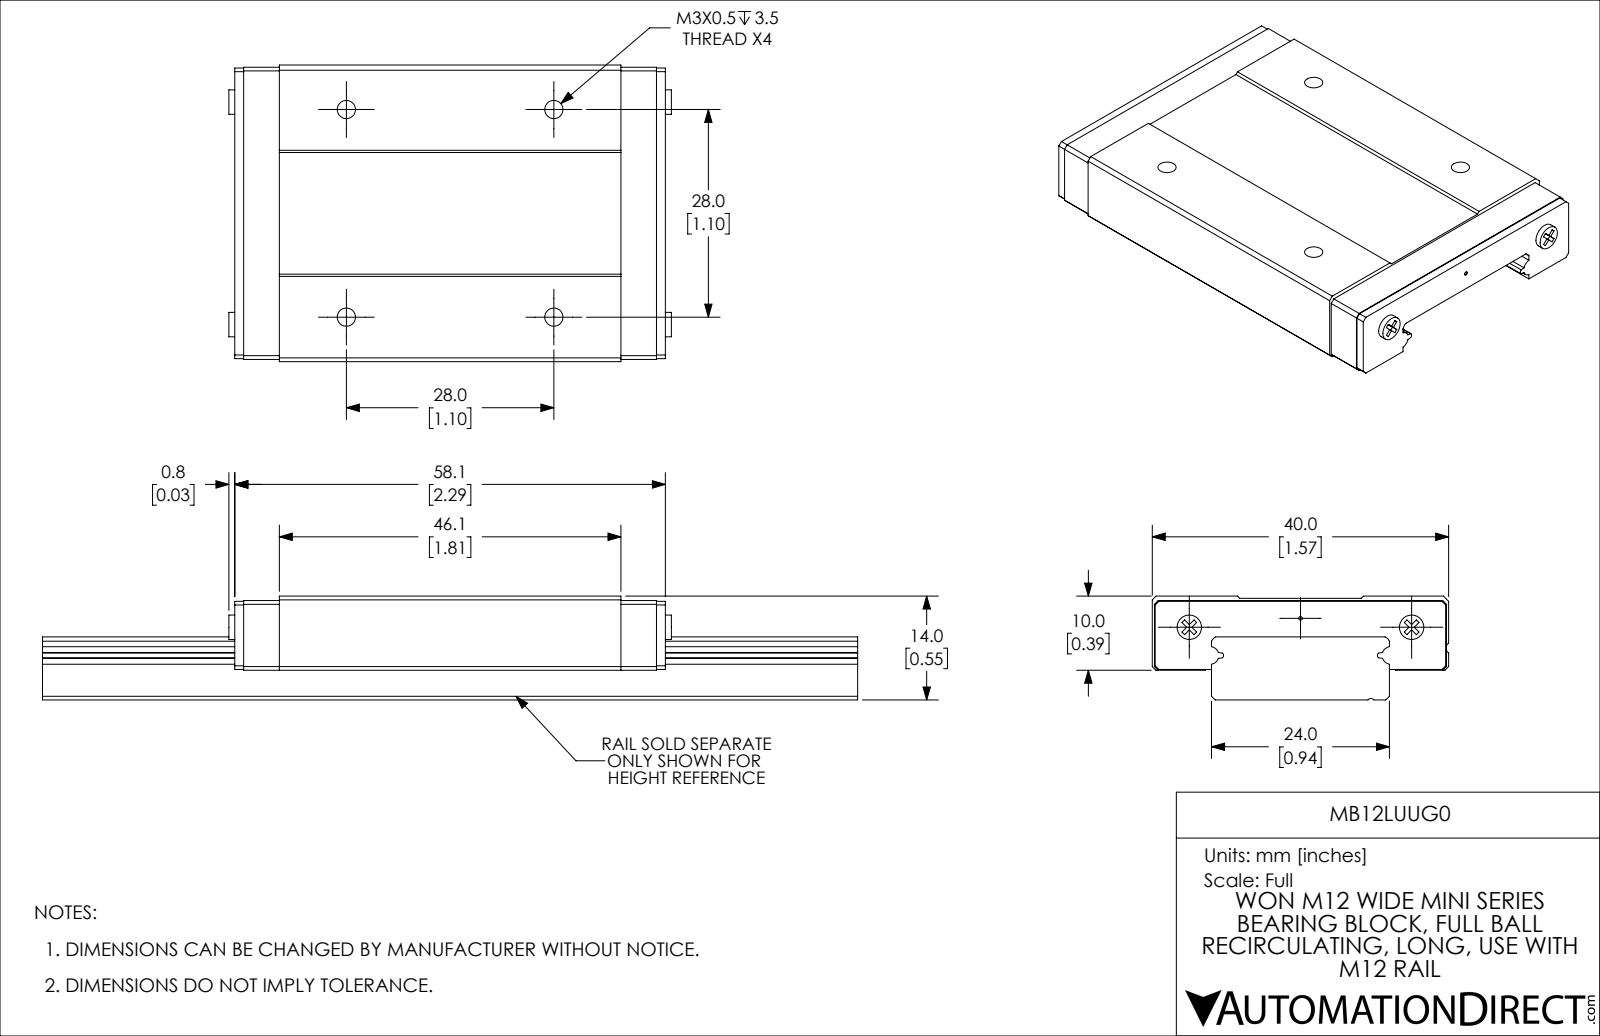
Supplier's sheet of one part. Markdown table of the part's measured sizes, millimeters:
| quantity | value |
| --- | --- |
| part name | MB12LUUG0 |
| STEP written by | SolidWorks 2019 (CONFIG_CONTROL_DESIGN) |
| units | millimeters |
| bodies | 1 solid, 158 faces (120 planar, 30 cylindrical, 8 other) |
| overall size | 59.7 × 40 × 10 |
| volume | 16 521 mm³ |
| surface area | 7 196 mm² |
| round holes (diameter × count) | 2.46 × 4, 0.5 × 1 |
| round bosses / shafts (diameter × count) | 3.3 × 2 |
| partial cylindrical surfaces (radius × count) | 0.42 × 2, 1.15 × 2, 1.2 × 2, 0.8 × 1 |
| main face-to-face distances | 5.5, 5.2, 4.5, 9.7, 10, 9.4, 4.9, 0.6, 40, 58.1 |
| hole center spacings | 28, 39.6 |
